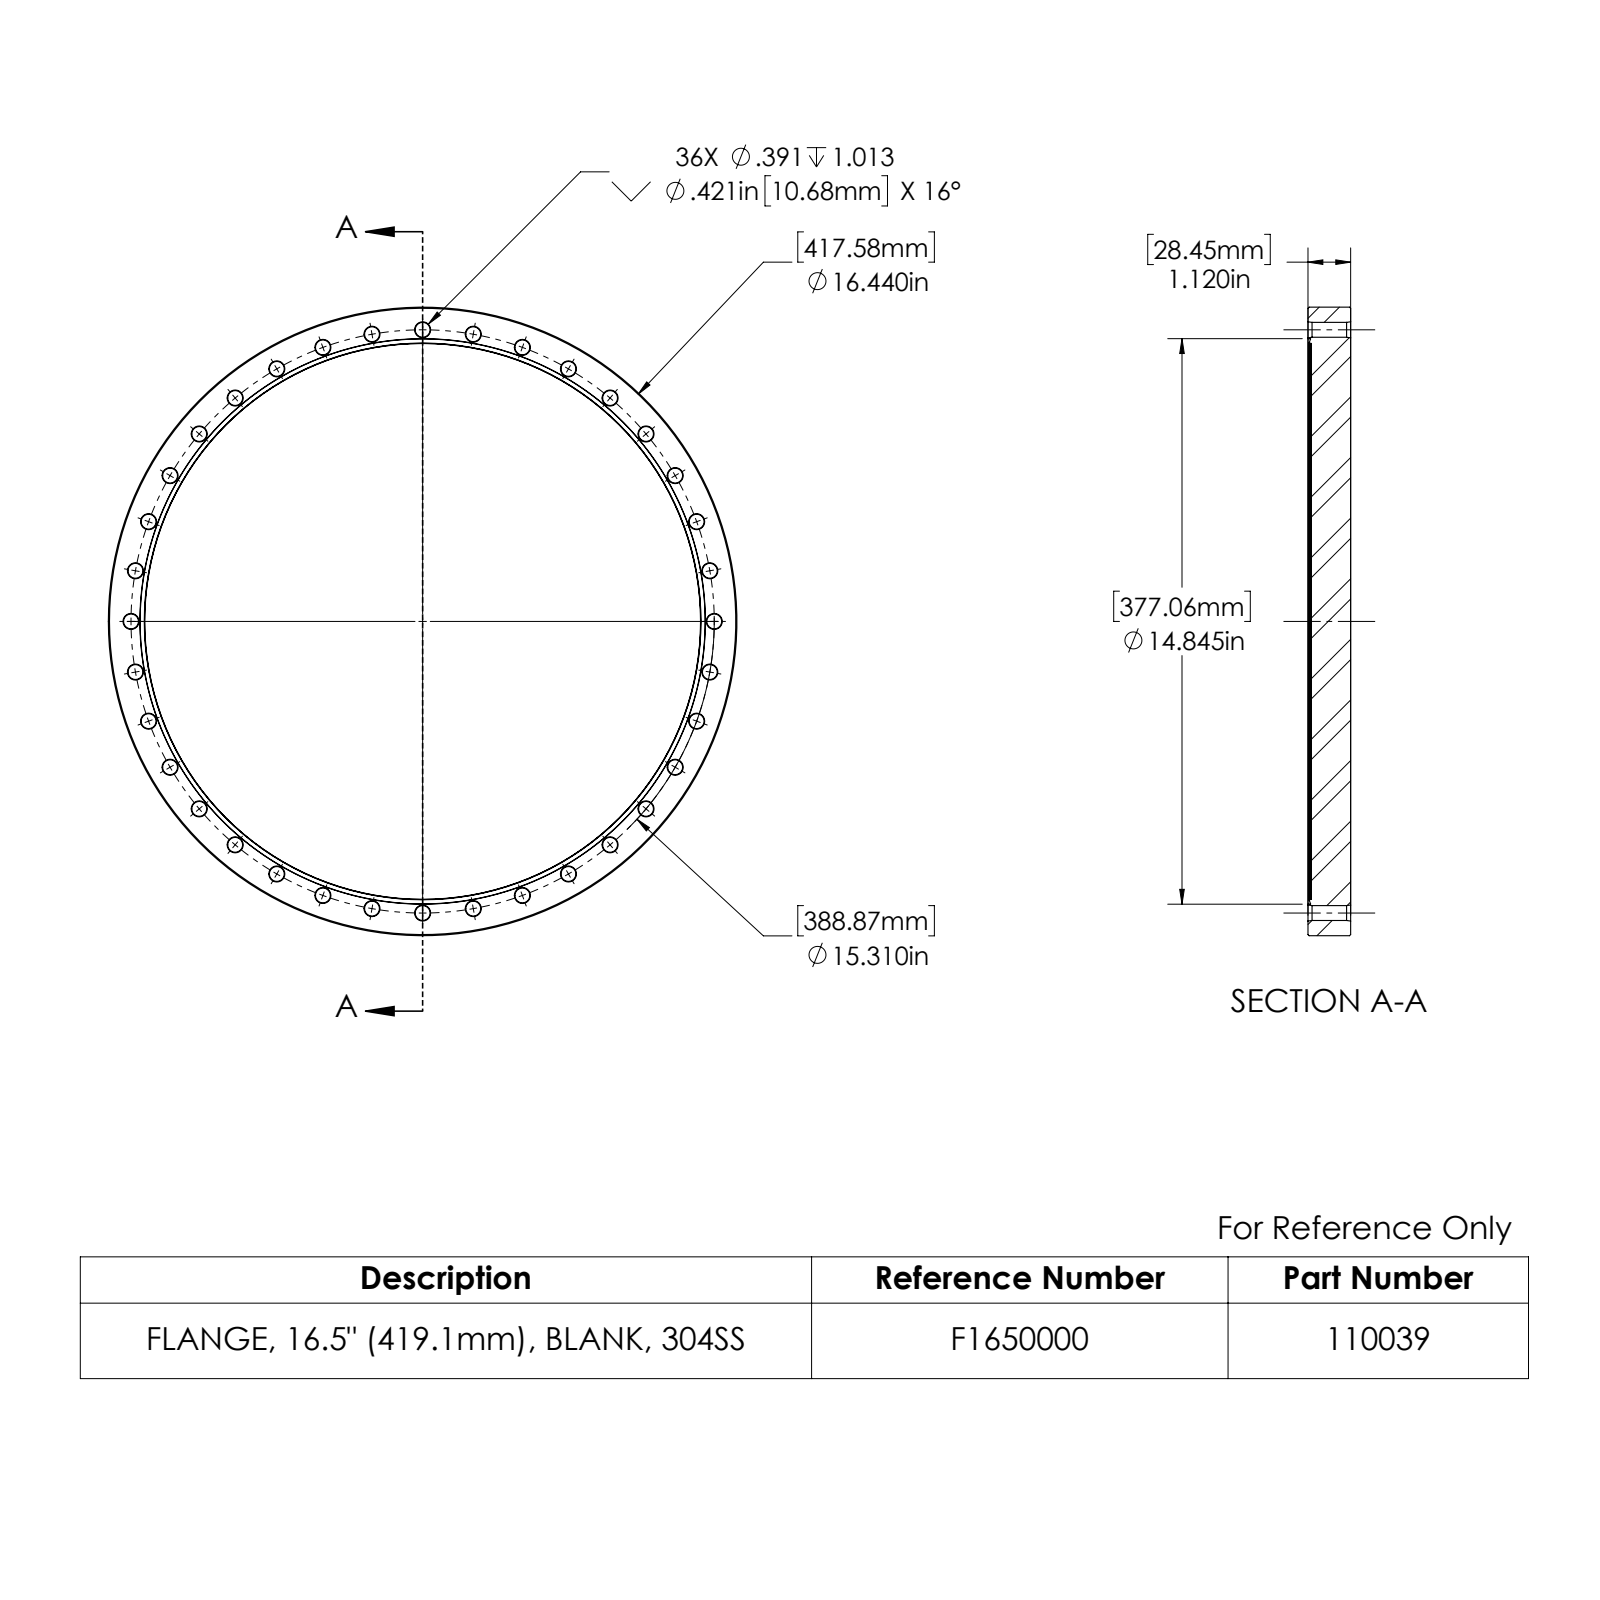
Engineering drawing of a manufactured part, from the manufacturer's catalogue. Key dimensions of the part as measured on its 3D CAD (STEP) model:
Part name (STEP PRODUCT): 110039
STEP written by: SolidWorks 2022 (AUTOMOTIVE_DESIGN)
Units: inches
Bodies: 1 solid, 237 faces (3 planar, 78 cylindrical, 156 other)
Overall size (bounding box): 16.5 × 16.5 × 1.12
Volume: 220.9 in³ · Surface area: 529.4 in²
Round holes (diameter × count): ⌀0.391 ×36, ⌀14.6 ×1, ⌀14.845 ×1
Round bosses / shafts (diameter × count): ⌀16.5 ×1
Main face-to-face distances: 1.04, 0.08, 1.12
Hole centre spacings: 1.334, 2.659, 8.781, 13.876, 3.963, 12.541, 5.236, 6.47
